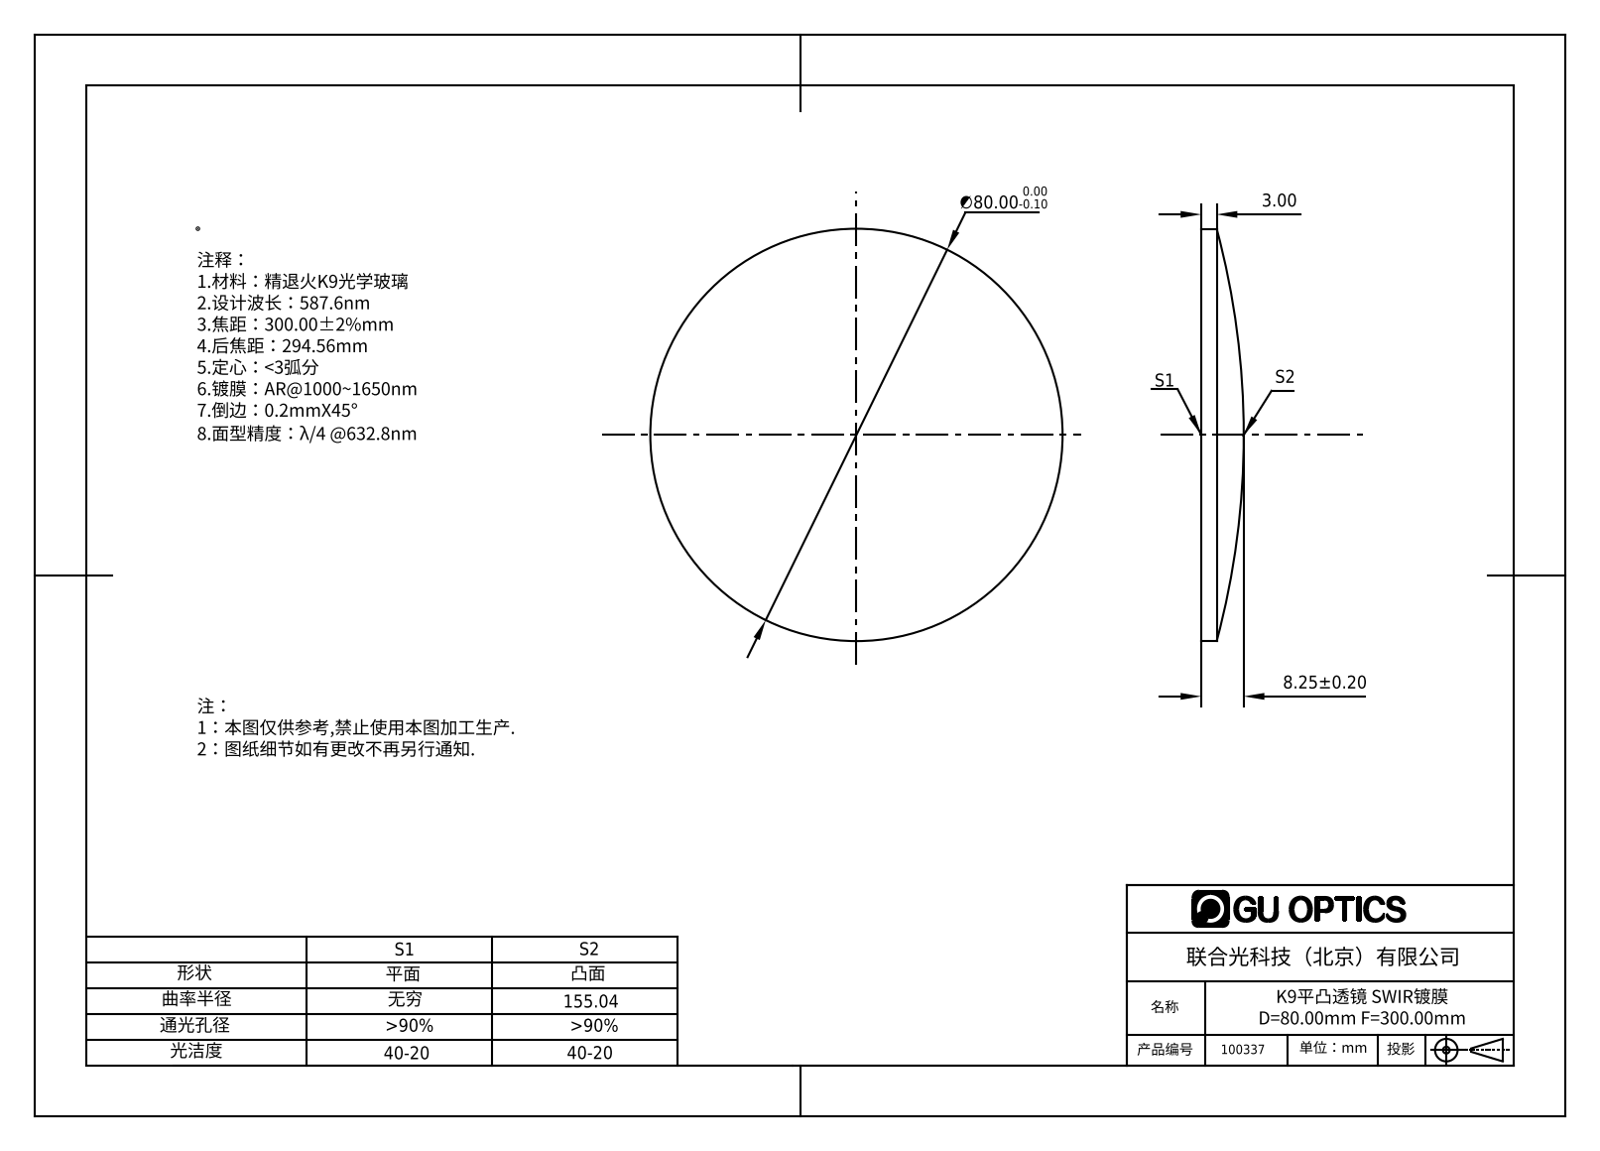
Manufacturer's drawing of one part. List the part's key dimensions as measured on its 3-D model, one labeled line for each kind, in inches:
Part name (STEP PRODUCT): 100165
STEP written by: SolidWorks 2016 (AUTOMOTIVE_DESIGN)
Units: inches
Bodies: 1 solid, 5 faces (1 planar, 2 cylindrical, 2 other)
Overall size (bounding box): 3.15 × 3.15 × 0.325
Volume: 1.73 in³ · Surface area: 16.89 in²
Round bosses / shafts (diameter × count): ⌀3.15 ×1
